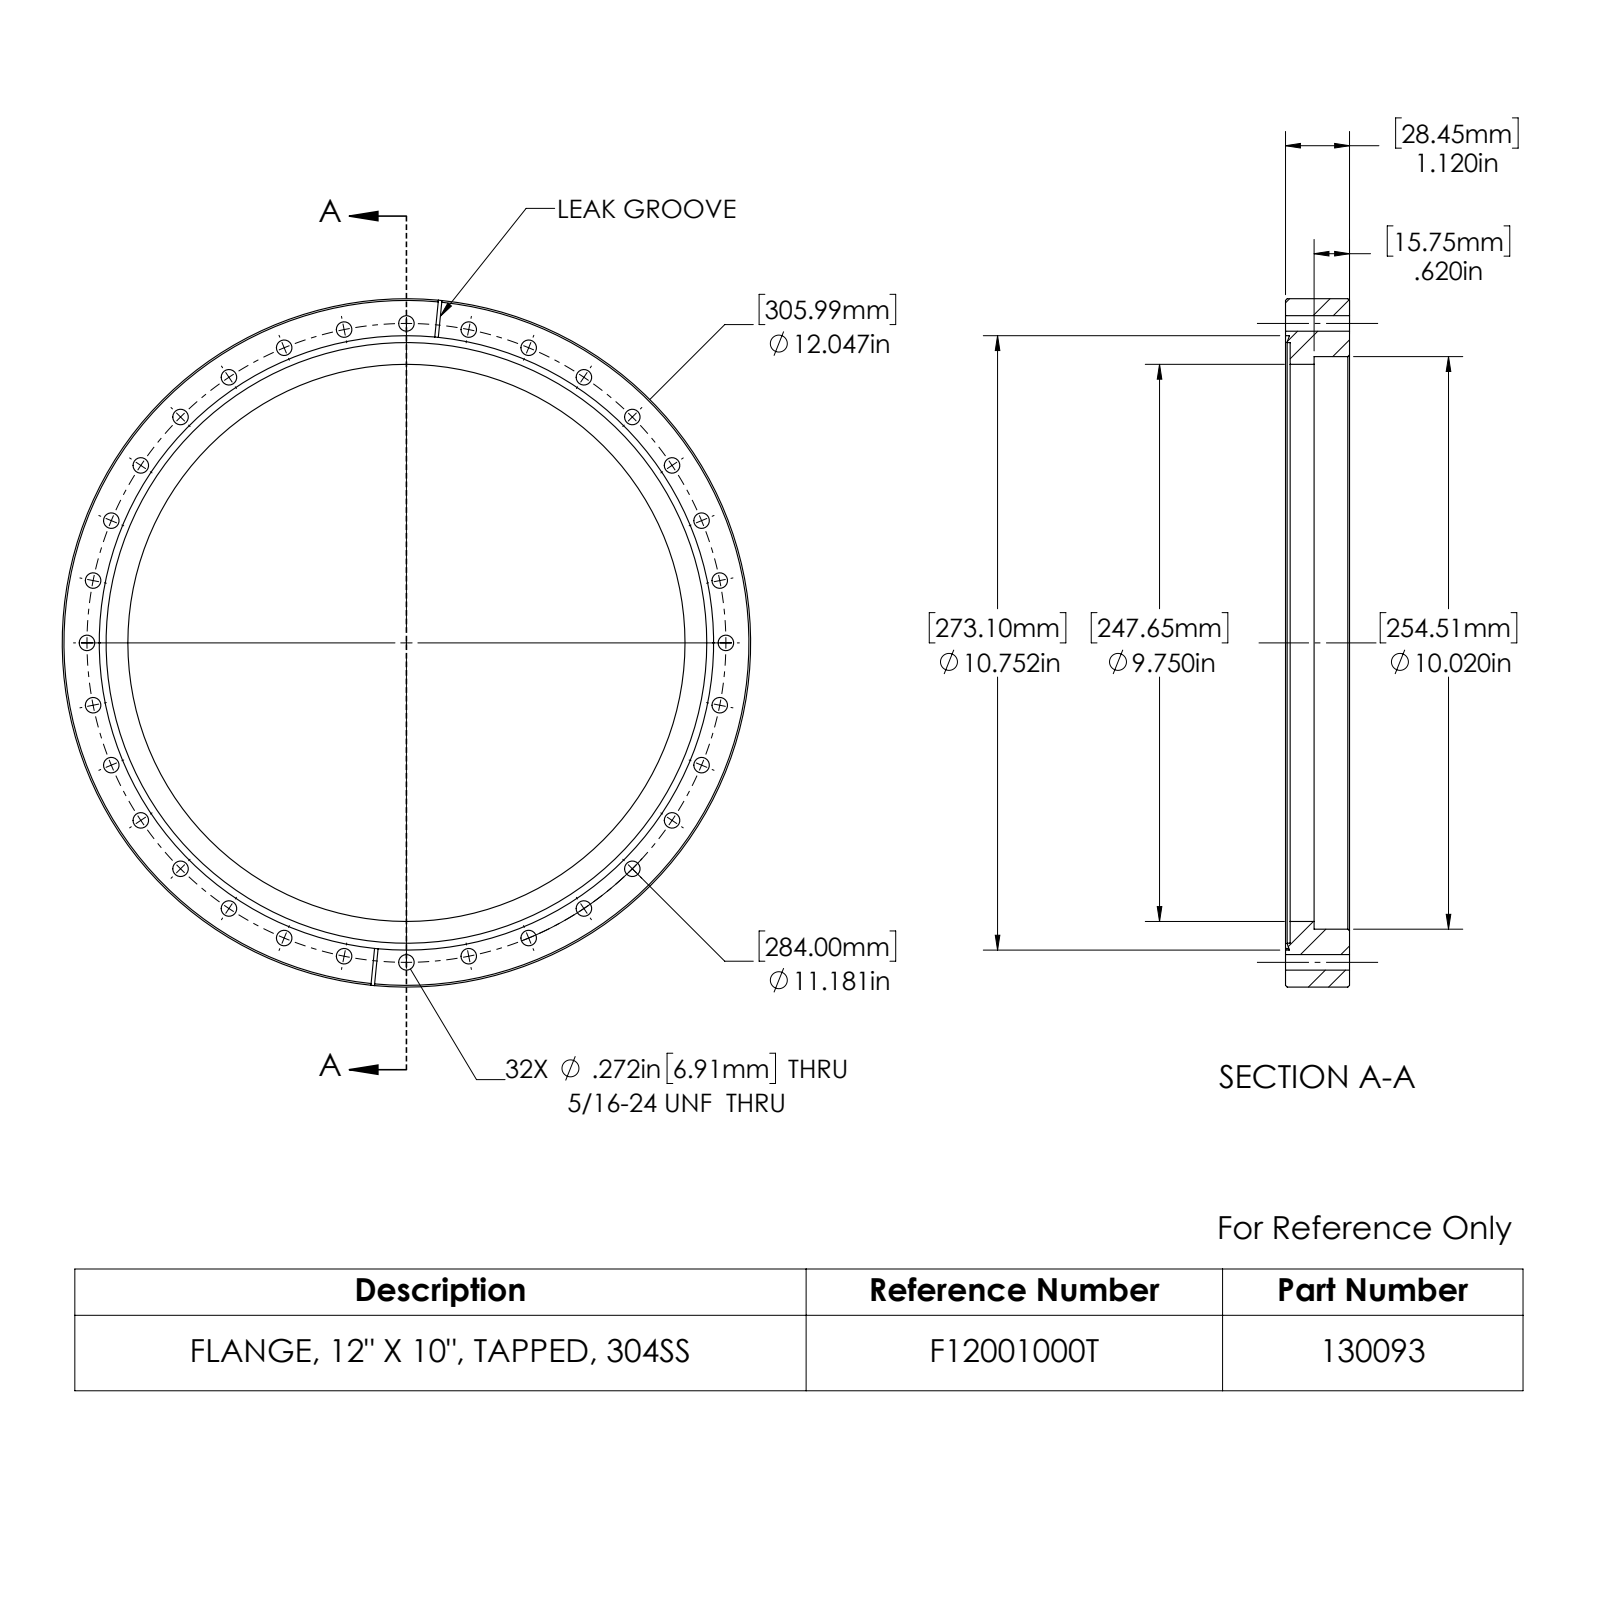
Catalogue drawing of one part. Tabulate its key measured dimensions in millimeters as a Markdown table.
| quantity | value |
| --- | --- |
| part name | 130093_A |
| STEP written by | SolidWorks 2022 (CONFIG_CONTROL_DESIGN) |
| units | millimeters |
| bodies | 1 solid, 100 faces (9 planar, 76 cylindrical, 15 other) |
| overall size | 306 × 306 × 28.4 |
| volume | 624 800 mm³ |
| surface area | 117 900 mm² |
| round holes (diameter × count) | 6.9 × 32, 247.7 × 1, 254.5 × 1, 267 × 1, 273.1 × 1 |
| round bosses / shafts (diameter × count) | 306 × 1 |
| partial cylindrical surfaces (radius × count) | 31.8 × 2 |
| main face-to-face distances | 28.4, 26.4, 2.1, 15.7, 10.6, 12.7, 1.6 |
| hole center spacings | 82.4, 157.8, 200.8, 262.4, 271.8, 278.5, 282.6, 236.1 |
